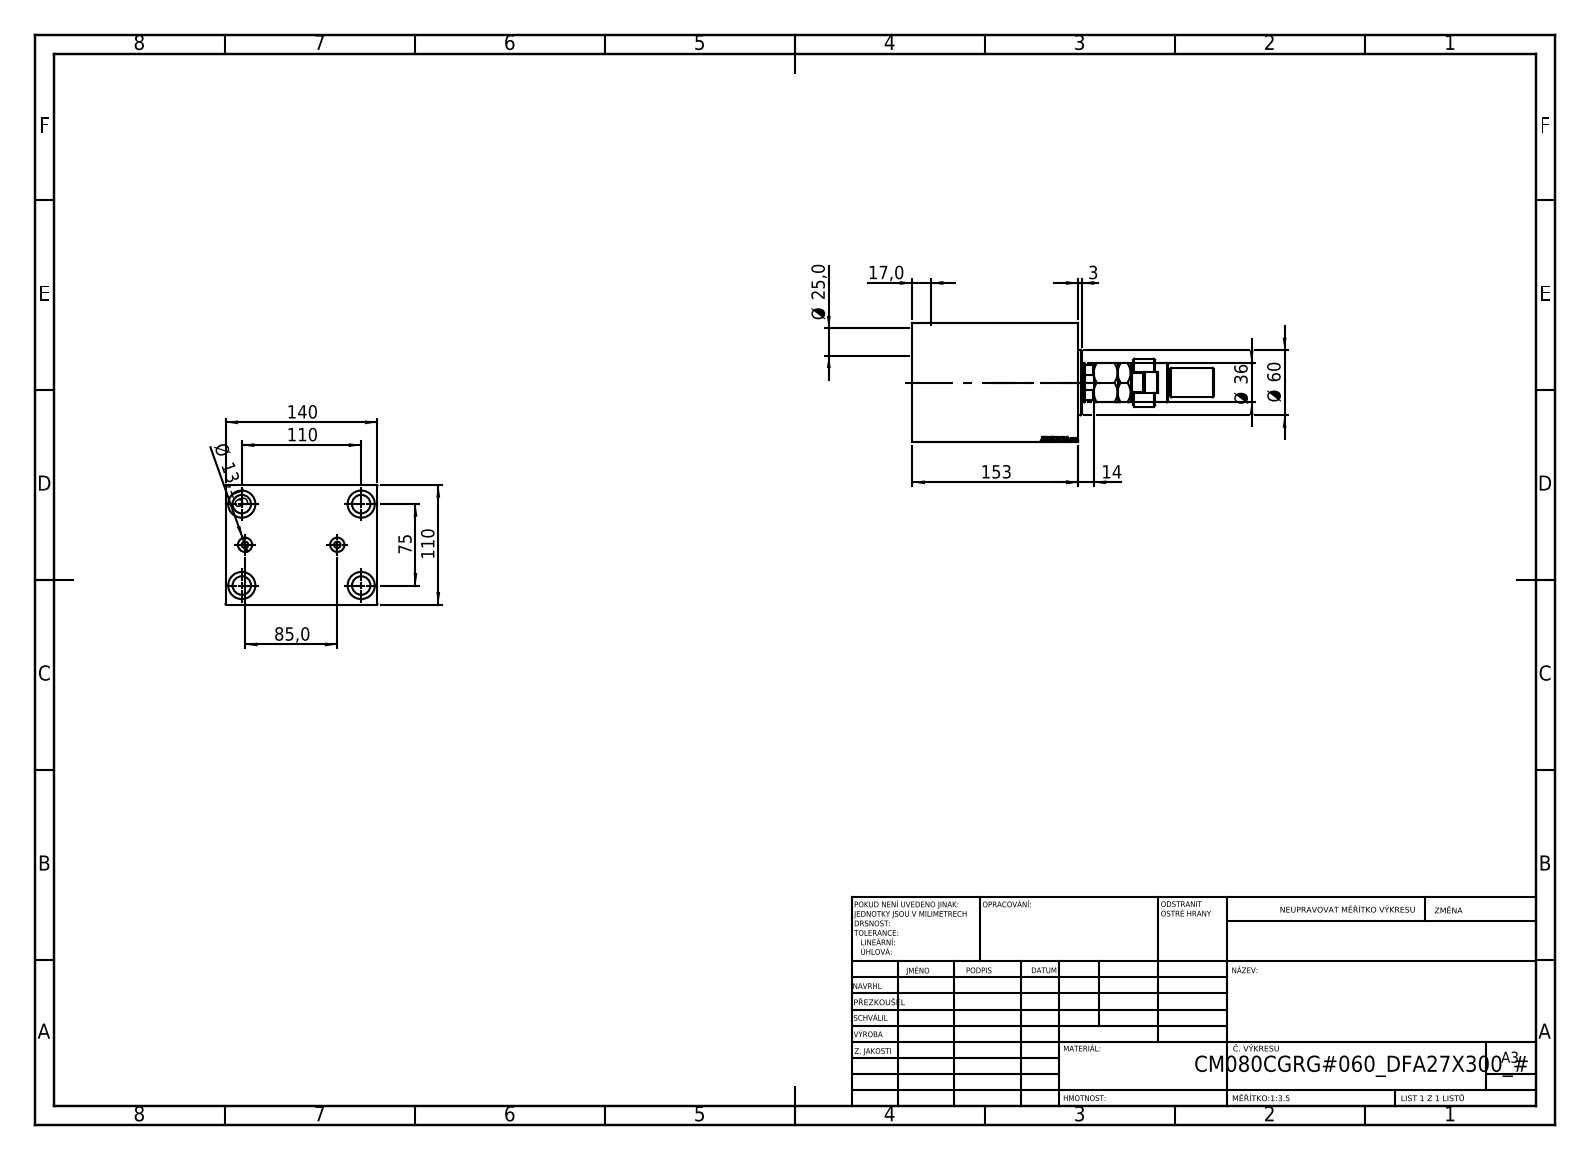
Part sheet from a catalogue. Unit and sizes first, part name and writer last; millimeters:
Units: millimetres
Overall size (bounding box): 277.5 × 140 × 110
Round holes (diameter × count): ⌀17 ×4, ⌀25 ×4, ⌀6 ×2, ⌀13.16 ×2, ⌀25.5 ×1, ⌀39.5 ×1, ⌀80 ×1, ⌀82 ×1, ⌀87 ×1
Round bosses / shafts (diameter × count): ⌀60 ×1, ⌀44 ×1, ⌀36 ×1, ⌀28 ×1, ⌀27 ×1, ⌀25 ×1, ⌀18 ×1
Partial cylindrical surfaces — rounded edges, fillets, slot ends (radius × count): R9.5 ×1, R15 ×1, R17.5 ×1
Main face-to-face distances: 110, 140, 153, 132, 21, 14, 139, 118, 74, 60
Hole centre spacings: 66.57, 37.62, 43.48, 75, 95.66, 110, 113.38, 133.14
Volume: 2 033 000 mm³ · Surface area: 252 506 mm²
Bodies: 5 solids, 945 faces (436 planar, 71 cylindrical, 438 other)
Part name (STEP PRODUCT): MFA; V450CM_C_Body; V450CM_VC_B; FEMALE_PART_FOR_DFA (+1 more)
STEP written by: SolidWorks 2019 (CONFIG_CONTROL_DESIGN)
